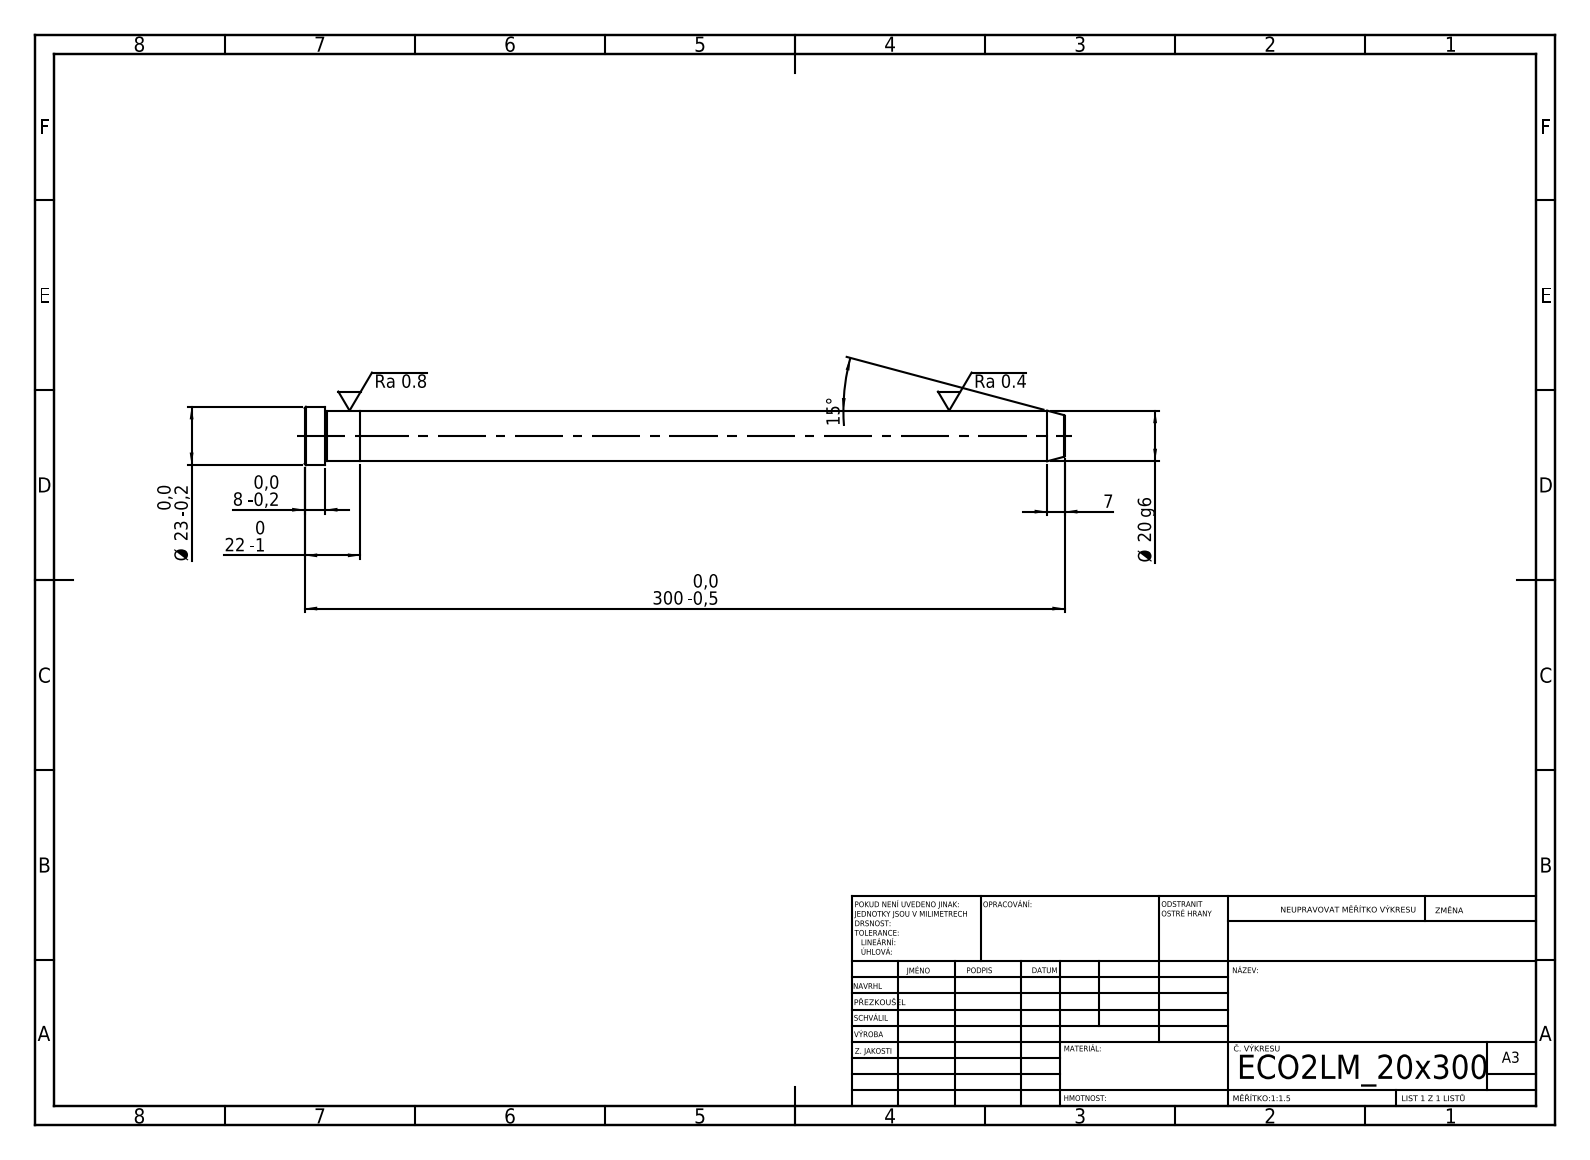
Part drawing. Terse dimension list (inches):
written by: SolidWorks 2019 (CONFIG_CONTROL_DESIGN)
unit: in
bodies: 2 solids, 21 faces (5 planar, 6 cylindrical, 10 other)
size: 11.811 × 0.906 × 0.906
volume: 5.775 in³; area: 31.4 in²
bosses: 1× ⌀0.906, 1× ⌀0.787
face distances: 0.866, 10.945, 11.811, 11.496, 0.551, 0.315
